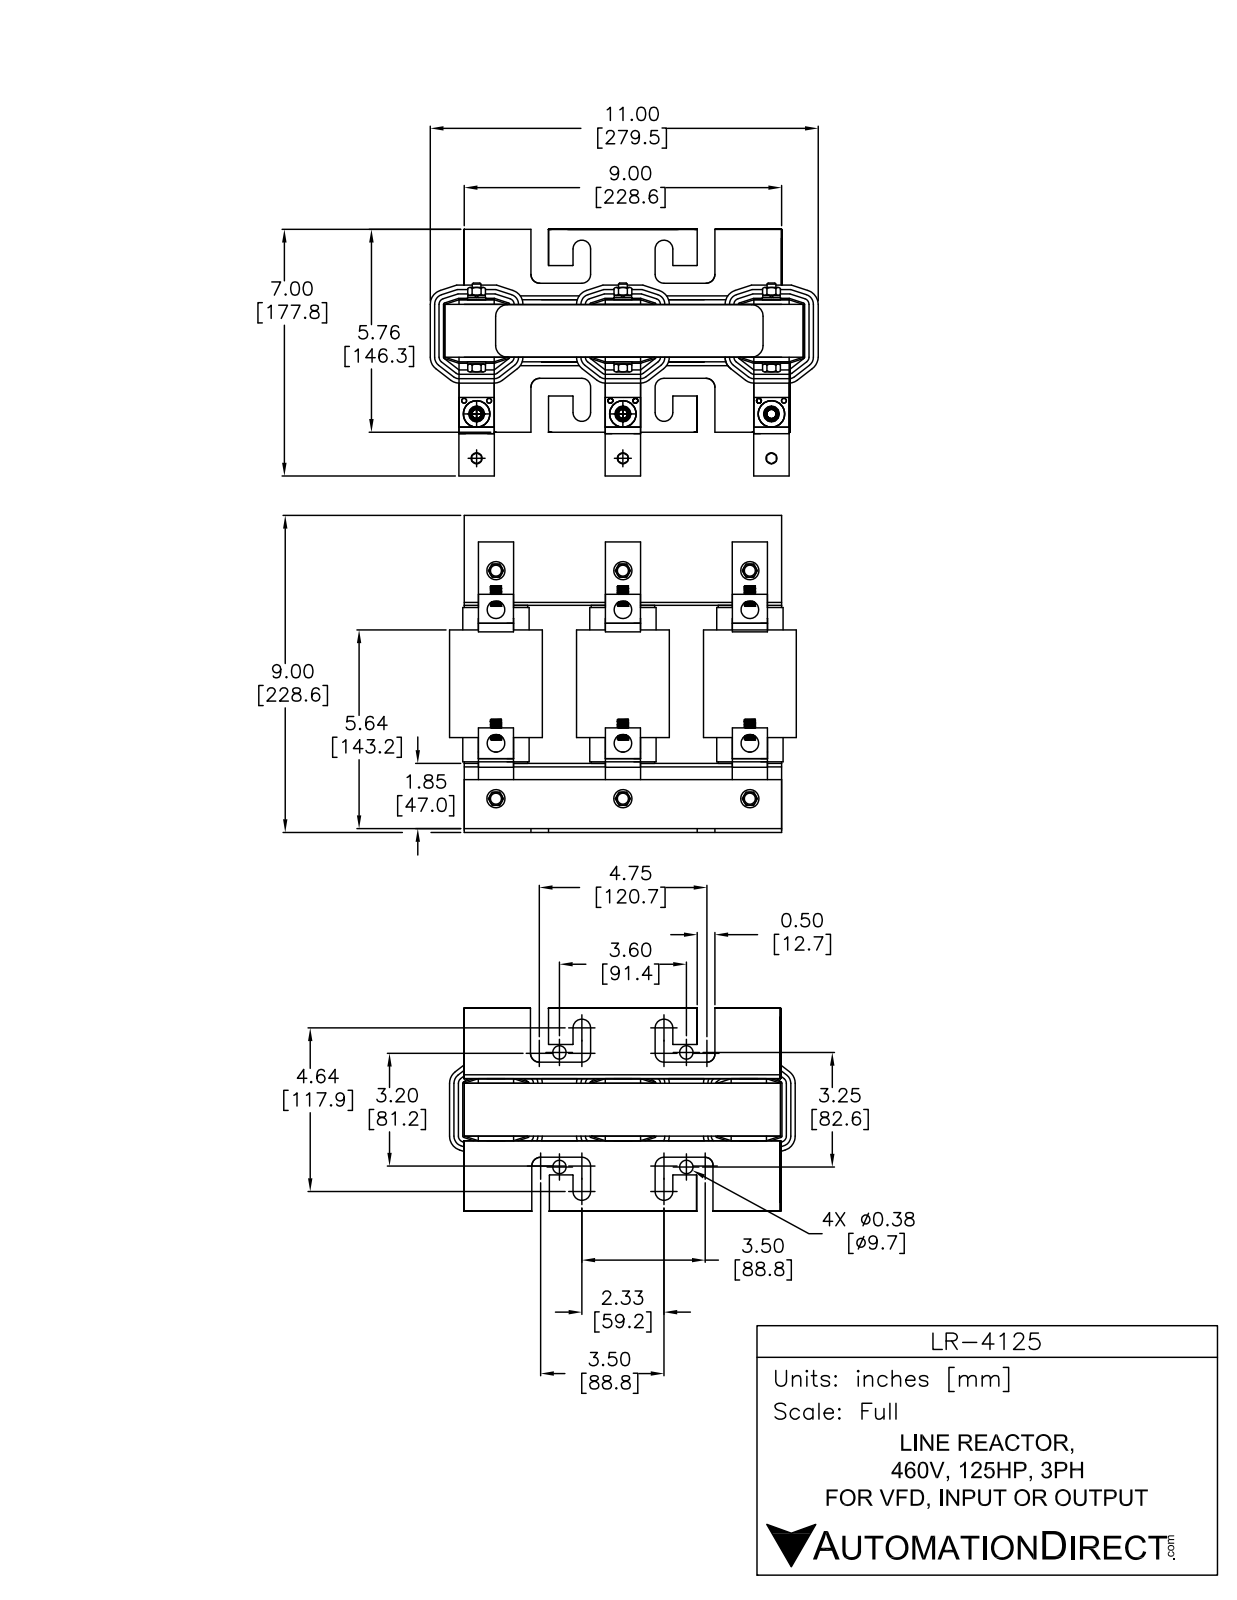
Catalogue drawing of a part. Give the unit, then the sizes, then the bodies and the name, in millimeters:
Units: millimetres
Overall size (bounding box): 259.68 × 209.59 × 176.28
Round holes (diameter × count): ⌀16 ×9, ⌀3.51 ×6, ⌀15.61 ×3
Round bosses / shafts (diameter × count): ⌀6.25 ×8, ⌀19 ×6, ⌀13.08 ×6, ⌀11.81 ×6
Partial cylindrical surfaces — rounded edges, fillets, slot ends (radius × count): R10.54 ×24, R6.54 ×18, R2.54 ×12, R5.53 ×12, R6.35 ×12, R9.53 ×12, R15.54 ×12, R0.25 ×8
Main face-to-face distances: 38.1, 91.44, 3.56, 41.66, 46.74, 0.76, 4.32, 42.42, 45.98, 4
Hole centre spacings: 91.44, 182.88, 91.57, 133.09, 4.94, 18, 96.71, 73.44
Volume: 3 275 000 mm³ · Surface area: 782 322 mm²
Bodies: 53 solids, 927 faces (675 planar, 252 cylindrical, 0 other)
Part name (STEP PRODUCT): LR-4150
STEP written by: SolidWorks 2011 (AUTOMOTIVE_DESIGN)
